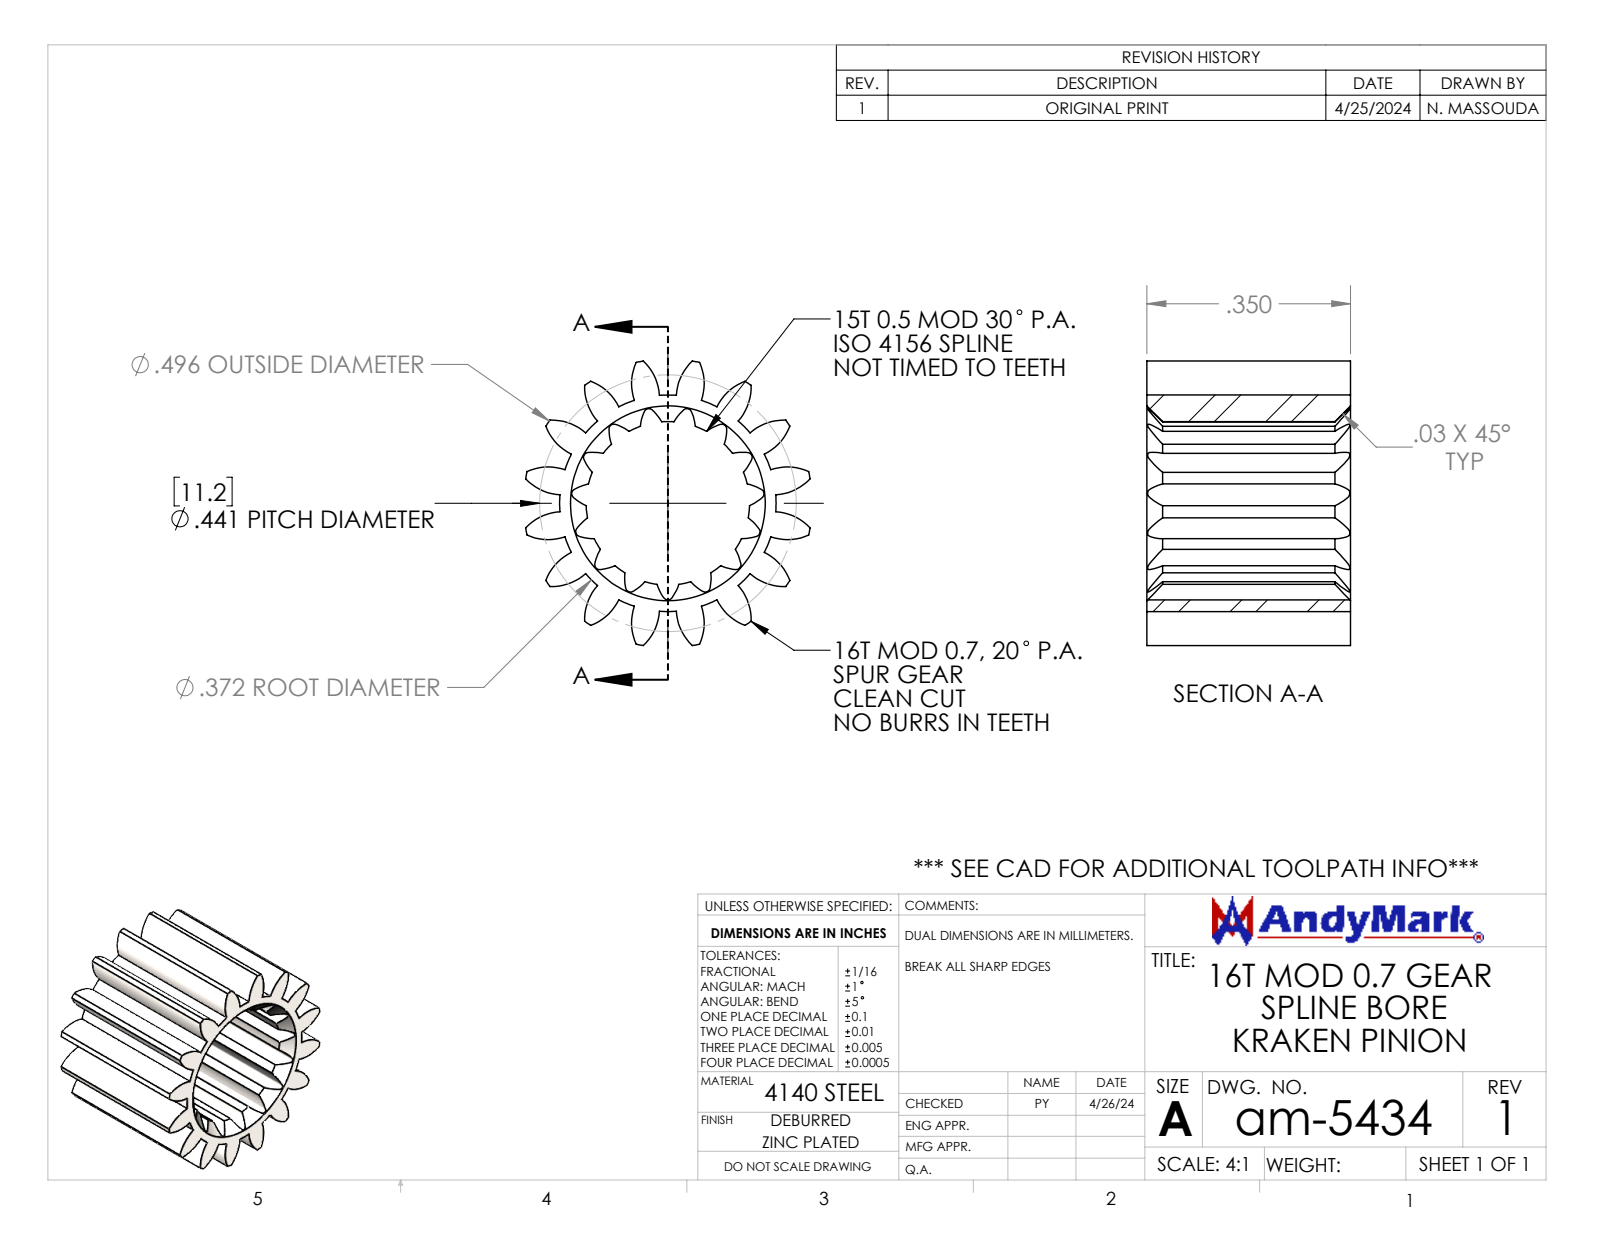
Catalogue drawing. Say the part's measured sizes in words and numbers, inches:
The part is named "am-5434 16T Mod 0.7 Gear Spline Bore Kraken Pinion". Its 3-D file was written by "SolidWorks 2024 (CONFIG_CONTROL_DESIGN)". It is 1 solid with 105 faces: 2 planar, 84 cylindrical and 19 other. Overall it measures 0.489 by 0.489 by 0.35 inches. Its volume is 0.026 cubic inches and its surface area 1.571 square inches. Partial cylindrical surfaces (rounded edges, fillets, slot ends): 32 of radius 0.088, 1 of radius 0.14, 1 of radius 0.186, 1 of radius 0.248. The main face-to-face distances are 0.35.
